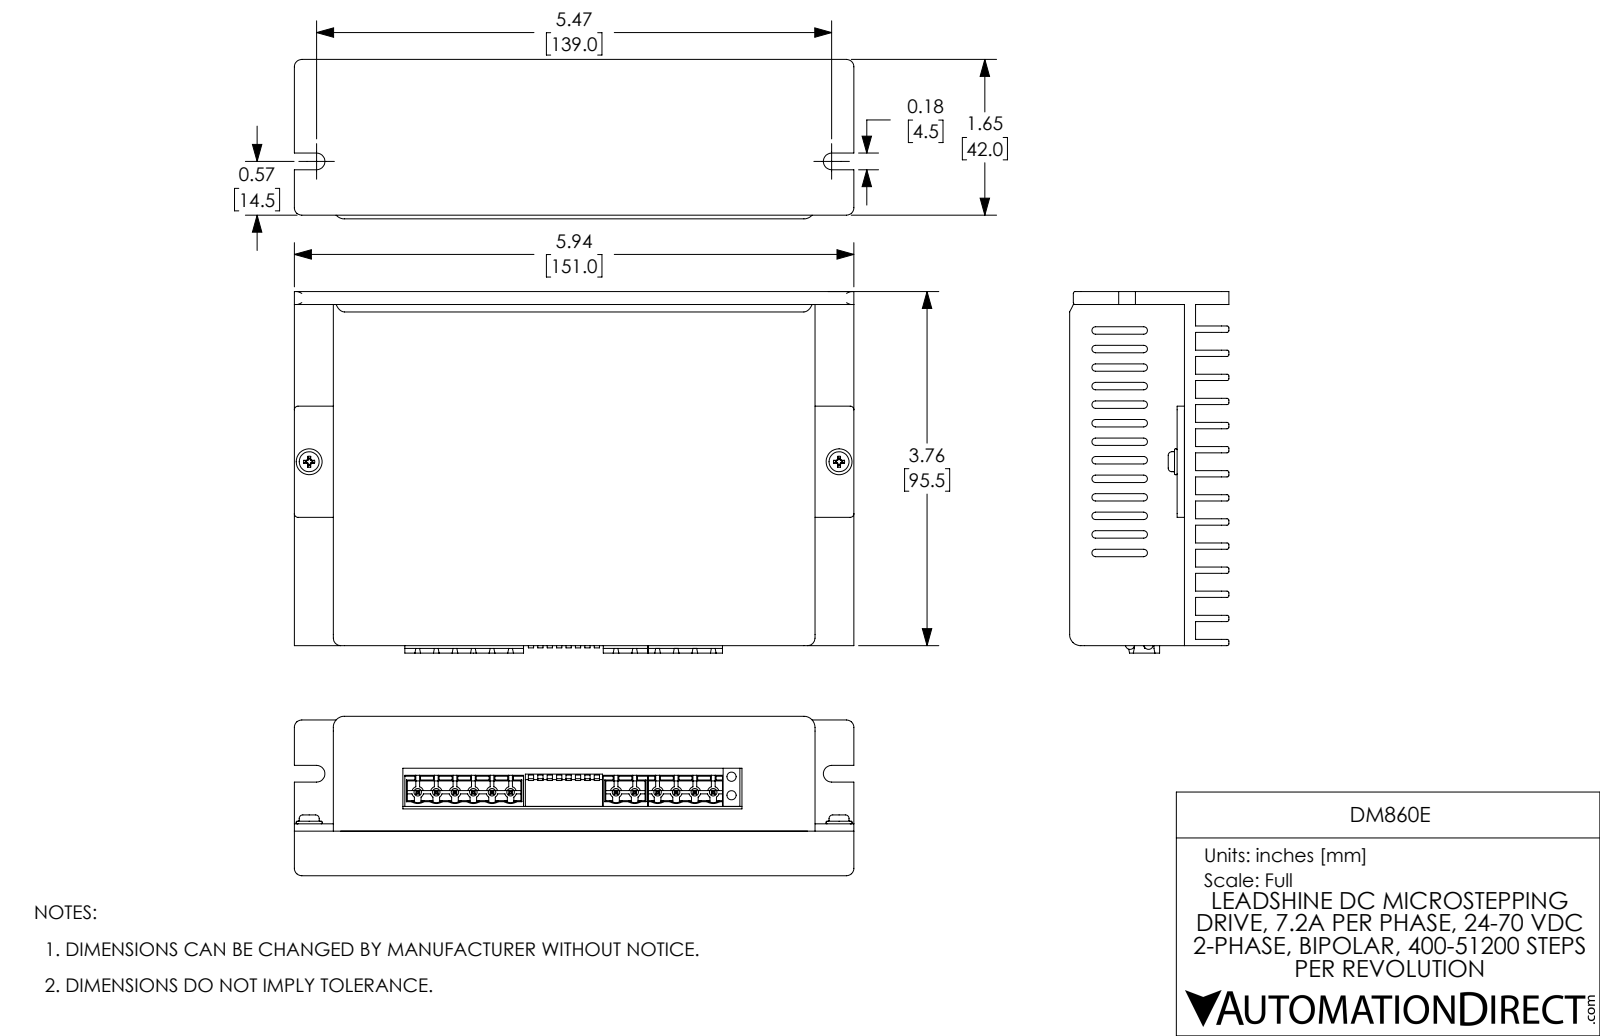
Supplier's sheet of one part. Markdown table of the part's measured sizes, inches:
| quantity | value |
| --- | --- |
| part name | DM860E_3D |
| STEP written by | SolidWorks 2017 (AUTOMOTIVE_DESIGN) |
| units | inches |
| bodies | 10 solids, 1440 faces (1041 planar, 335 cylindrical, 64 other) |
| overall size | 5.945 × 3.839 × 1.693 |
| volume | 10.65 in³ |
| surface area | 237 in² |
| round holes (diameter × count) | 0.08 × 12, 0.157 × 2, 0.118 × 1 |
| round bosses / shafts (diameter × count) | 0.276 × 2, 0.213 × 2, 0.118 × 2, 0.098 × 2, 0.093 × 2, 0.016 × 2 |
| partial cylindrical surfaces (radius × count) | 0.02 × 30, 0.039 × 30, 0.061 × 12, 0.11 × 12, 0.062 × 8, 0.079 × 6, 0.063 × 4, 0.118 × 3 |
| main face-to-face distances | 0.118, 1.22, 0.079, 0.256, 0.512, 0.957, 0.768, 1.024, 0.264, 0.185 |
| hole center spacings | 0.198, 0.591, 0.197, 0.394, 0.396, 0.639, 1.759, 1.909 |
